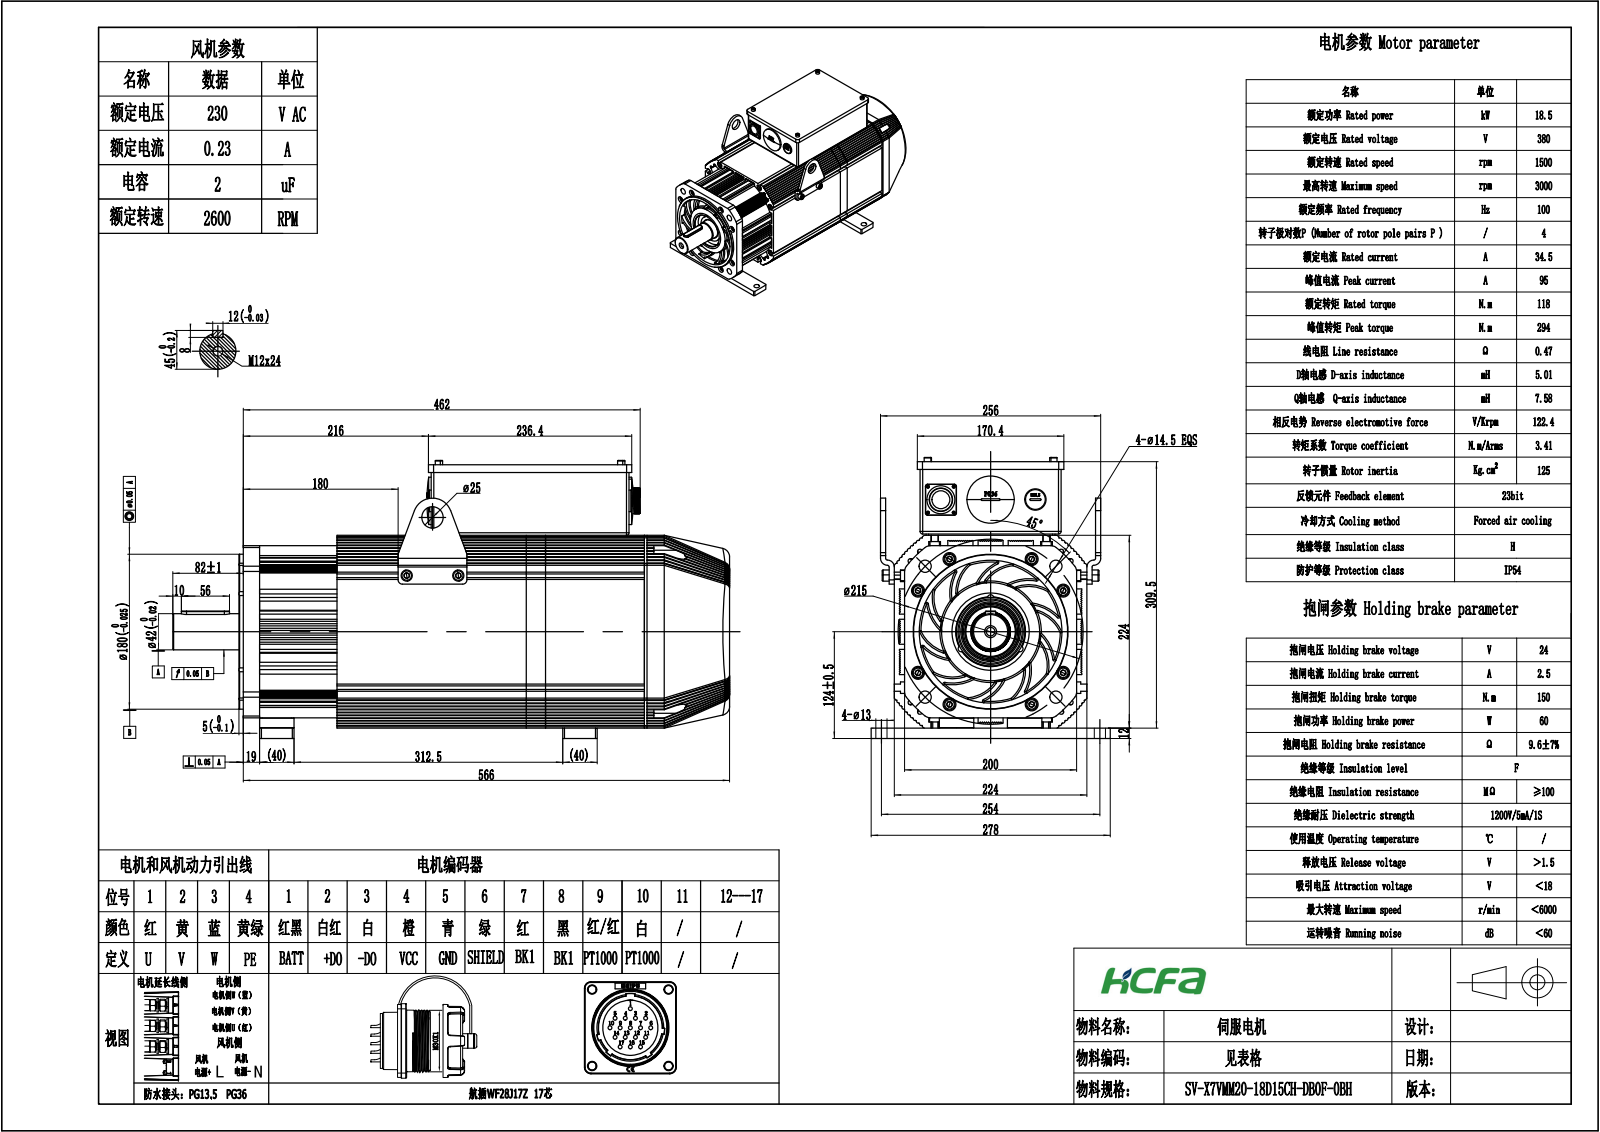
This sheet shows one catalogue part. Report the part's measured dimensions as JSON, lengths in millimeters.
{"part_name": "10002030101-0037-SV-X7VMM20-18D15CH-DB0F-0BH-5段外形图", "step_written_by": "SolidWorks 2021 (CONFIG_CONTROL_DESIGN)", "units": "millimeters", "bodies": {"solids": 8, "faces": 3828, "planar": 1637, "cylindrical": 1200, "other": 991}, "overall_size": [647.4, 326.5, 278], "volume_mm3": 24950000, "surface_area_mm2": 1193000, "round_holes": [[9, 24], [15, 14], [13, 8], [10, 6], [2.5, 4], [3.2, 4], [5.8, 4], [6.8, 4], [7, 4], [14.5, 4], [10.2, 1], [17, 1]], "round_bosses_or_shafts": [[1.5, 17], [13, 10], [8, 10], [8.5, 4], [6.3, 4], [5, 4], [40, 2], [180, 1]], "partial_cylinders_radius": [[2, 112], [1, 24], [1.5, 20], [5, 18], [1.4, 16], [3, 12], [0.2, 10], [10, 10]], "face_to_face_distances": [224, 2, 307.5, 12, 6, 309.5, 30, 194, 32, 192], "hole_center_spacings": [29.47, 43.17, 97, 124.07, 137.18, 138.41, 162.9, 167.15]}
